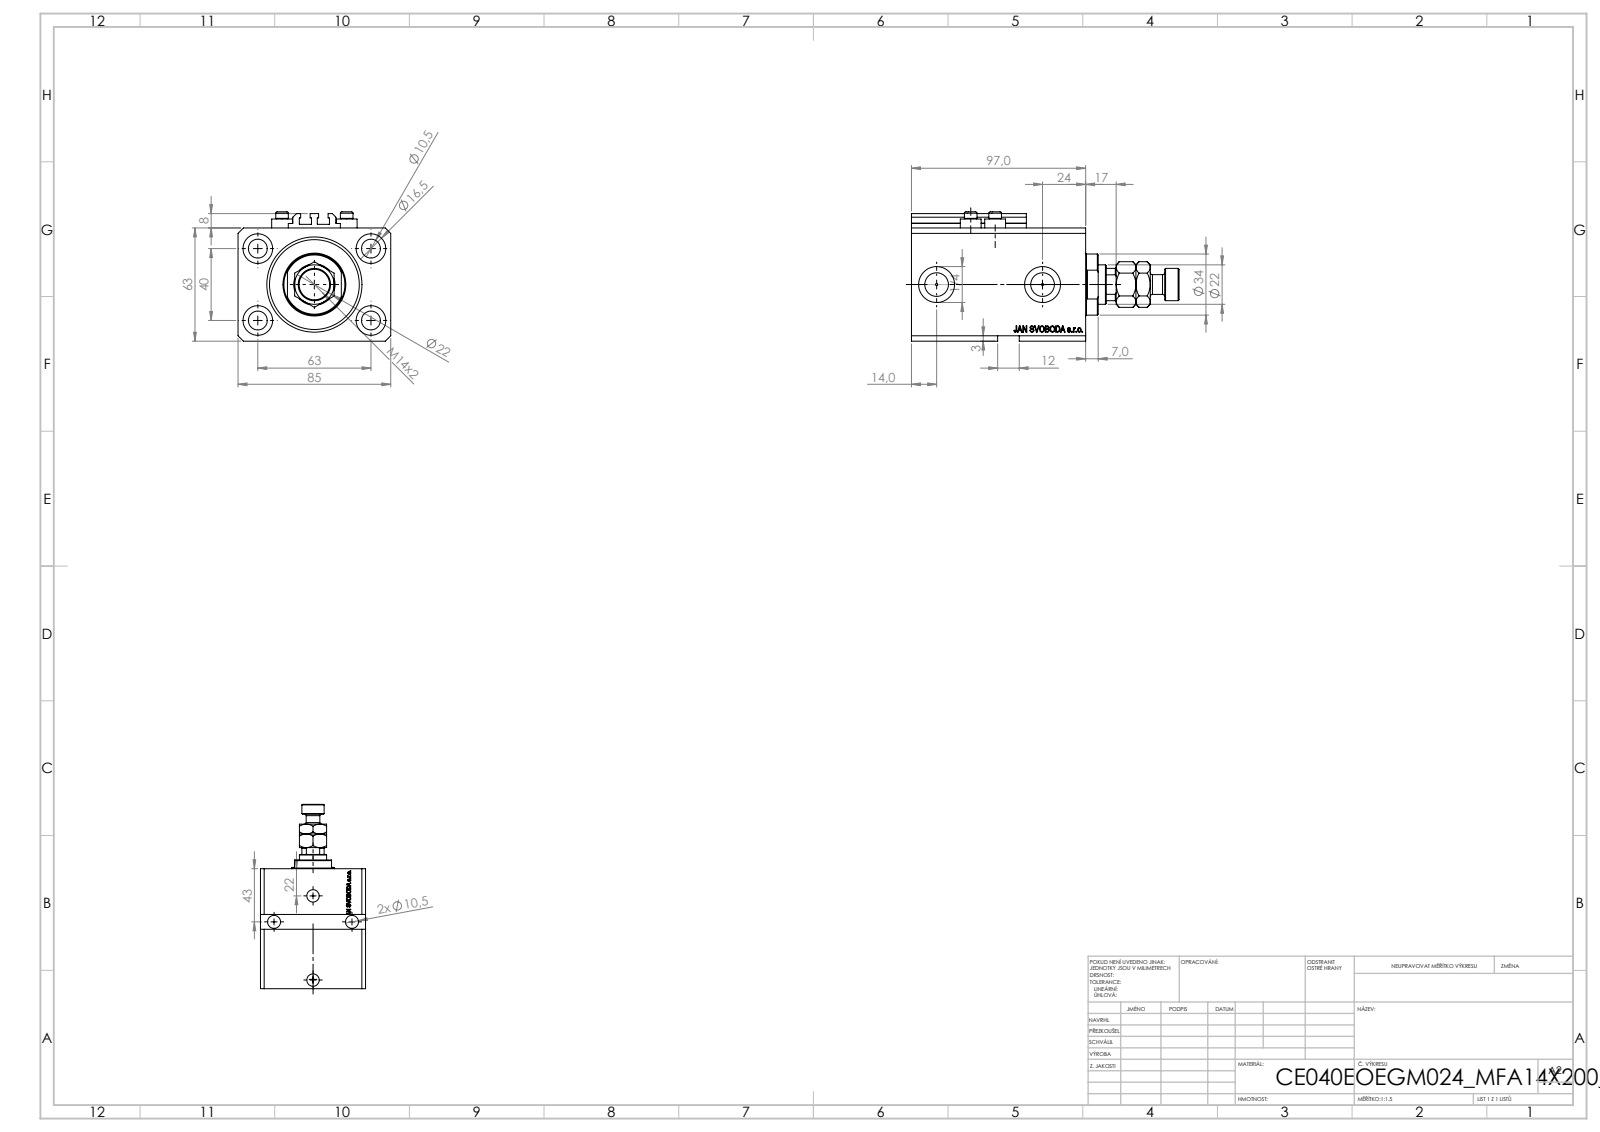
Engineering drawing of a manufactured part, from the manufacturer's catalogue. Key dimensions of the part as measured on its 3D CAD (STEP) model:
Part name (STEP PRODUCT): V250CE_VC_E; ALLEN BOLT V250CE; V250CE_E_Body; V250CE_C_VCP (+1 more)
STEP written by: SolidWorks 2019 (CONFIG_CONTROL_DESIGN)
Units: millimetres
Bodies: 9 solids, 1139 faces (551 planar, 130 cylindrical, 458 other)
Overall size (bounding box): 149 × 85 × 72
Volume: 464 902 mm³ · Surface area: 101 883 mm²
Round holes (diameter × count): ⌀10.5 ×6, ⌀1.25 ×4, ⌀4 ×4, ⌀16.5 ×4, ⌀10 ×2, ⌀13.16 ×2, ⌀20 ×2, ⌀12.5 ×1, ⌀22 ×1, ⌀40 ×1, ⌀53 ×1
Round bosses / shafts (diameter × count): ⌀11.6 ×4, ⌀7 ×4, ⌀34 ×1, ⌀18 ×1, ⌀11 ×1
Partial cylindrical surfaces — rounded edges, fillets, slot ends (radius × count): R0.2 ×10, R10.5 ×1
Main face-to-face distances: 63, 85, 17, 97, 80, 68.6, 11.4, 85.6, 3, 24
Hole centre spacings: 37.31, 63, 13.6, 15.4, 24.96, 31.19, 31.62, 33.62
